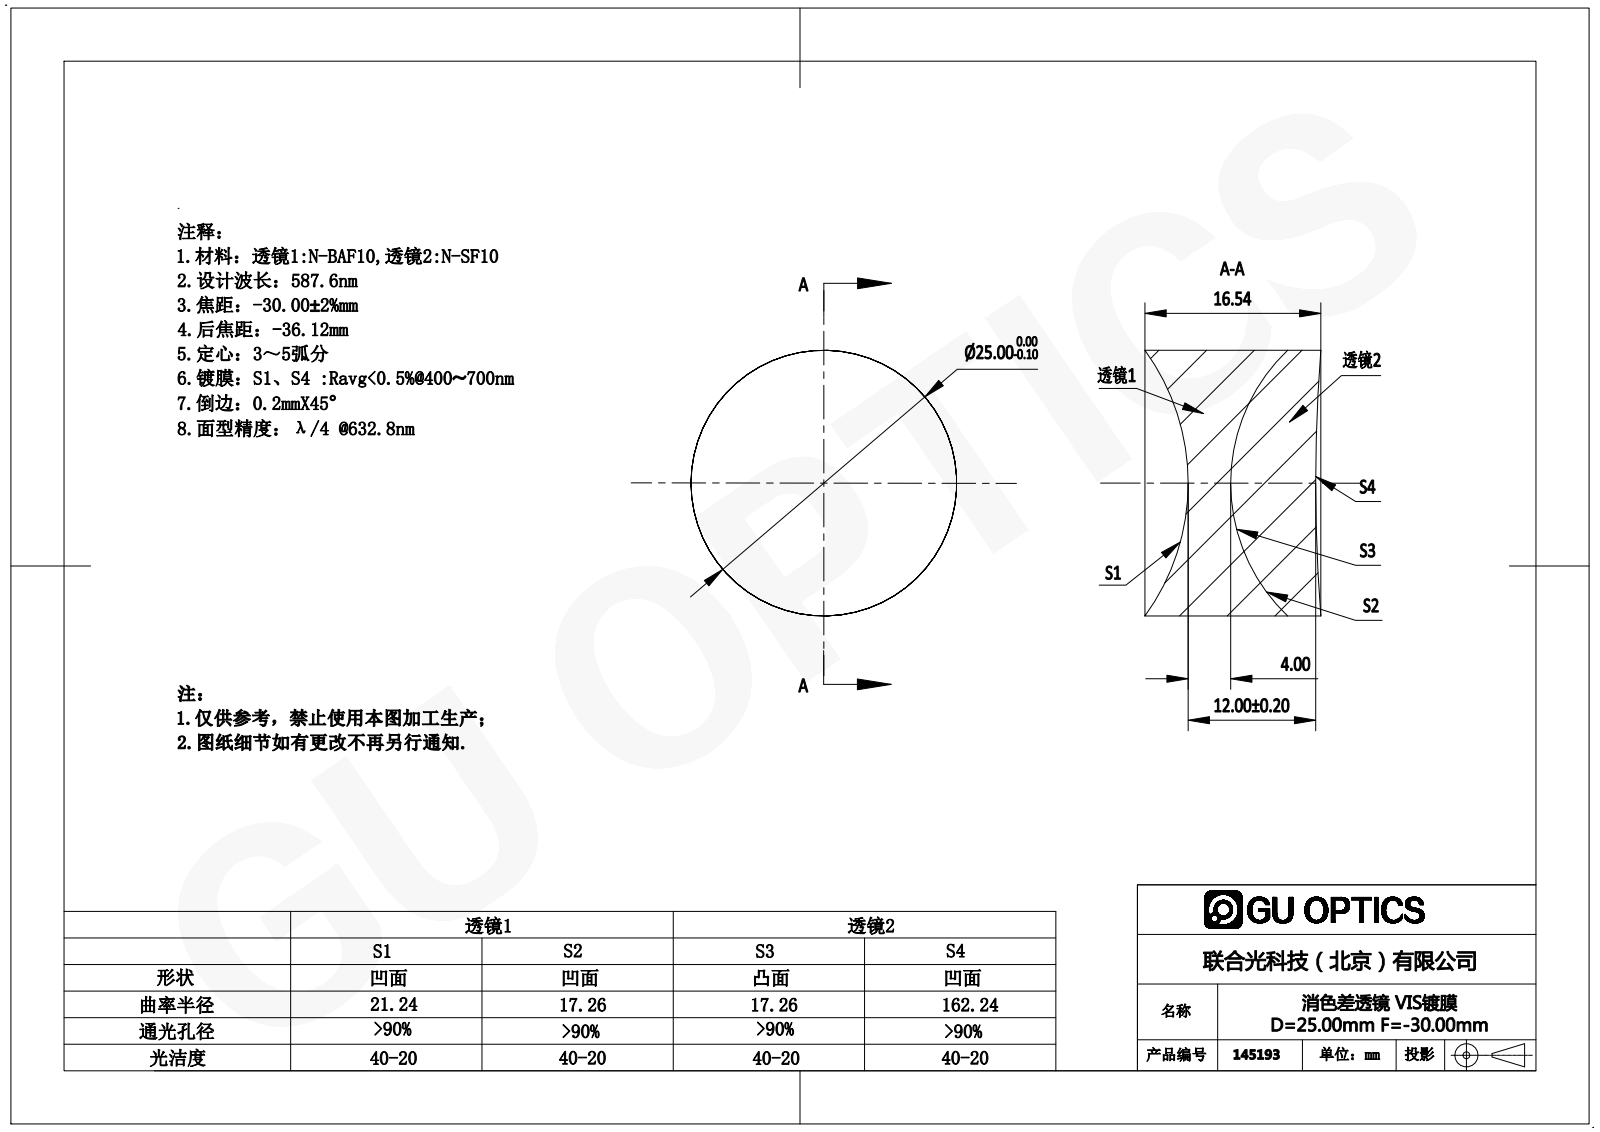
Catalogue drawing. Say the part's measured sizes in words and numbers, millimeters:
The part is named "145193". Its 3-D file was written by "SolidWorks 2016 (AUTOMOTIVE_DESIGN)". It is 2 solids with 12 faces: 0 planar, 4 cylindrical and 8 other. Overall it measures 25 by 25 by 16.55 millimeters. Its volume is 6 972 cubic millimeters and its surface area 3 496 square millimeters. Round bosses or shafts: 1 of diameter 25.
